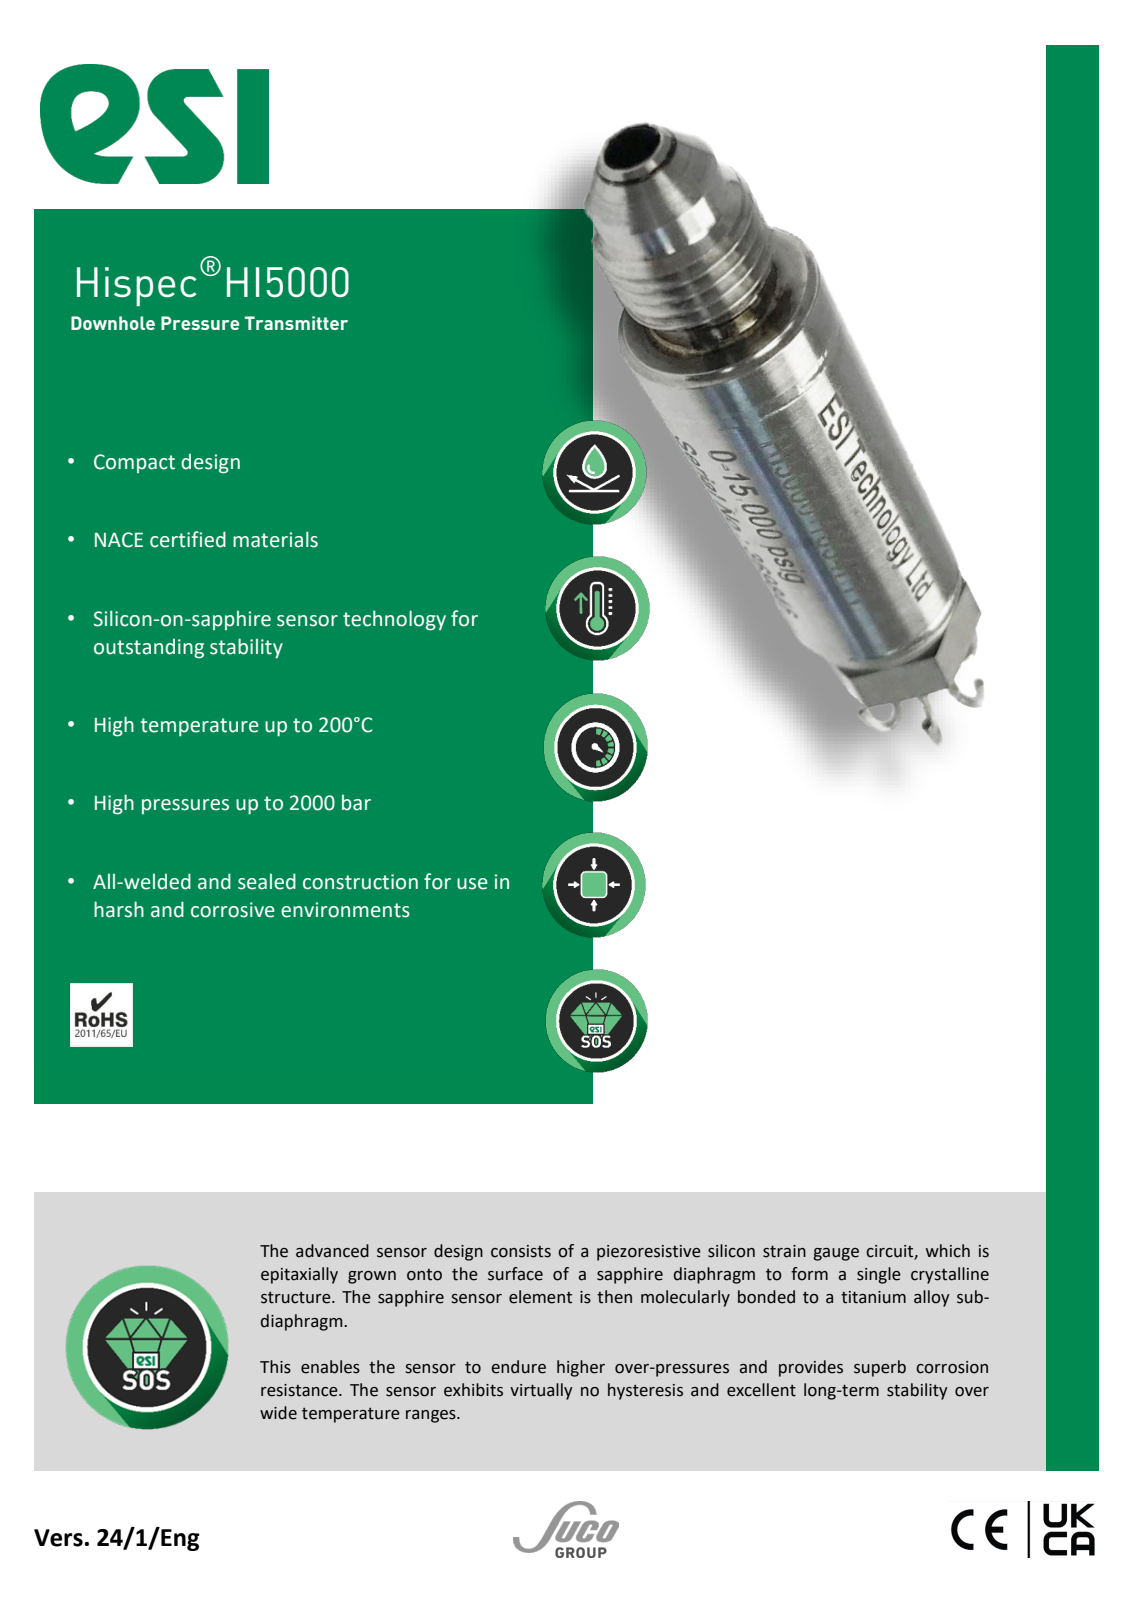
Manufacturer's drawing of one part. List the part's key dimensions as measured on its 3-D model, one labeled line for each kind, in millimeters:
Part name (STEP PRODUCT): p01; 9620-1; 9522_GlassBead.03; 9522_Pin.06 (+2 more)
STEP written by: PTC Creo Elements/Direct Modeling 19.0E 27-Jun-2016 (C) Parametric Technology GmbH (AUTOMOTIVE_DESIGN)
Units: millimetres
Bodies: 15 solids, 173 faces (45 planar, 96 cylindrical, 32 other)
Overall size (bounding box): 57.05 × 12.7 × 12.7
Volume: 5 550 mm³ · Surface area: 3 893 mm²
Round holes (diameter × count): ⌀0.76 ×6, ⌀2 ×6, ⌀2.2 ×1, ⌀3.18 ×1
Round bosses / shafts (diameter × count): ⌀0.76 ×8, ⌀2 ×2, ⌀12.7 ×1, ⌀11.7 ×1, ⌀11 ×1, ⌀10.7 ×1, ⌀10 ×1, ⌀9.53 ×1
Main face-to-face distances: 27, 1, 7, 34, 11.1, 26, 8, 38.03, 31.03, 30.03
Hole centre spacings: 2.75, 4.76, 5.5, 4.77, 2.76, 5.49
